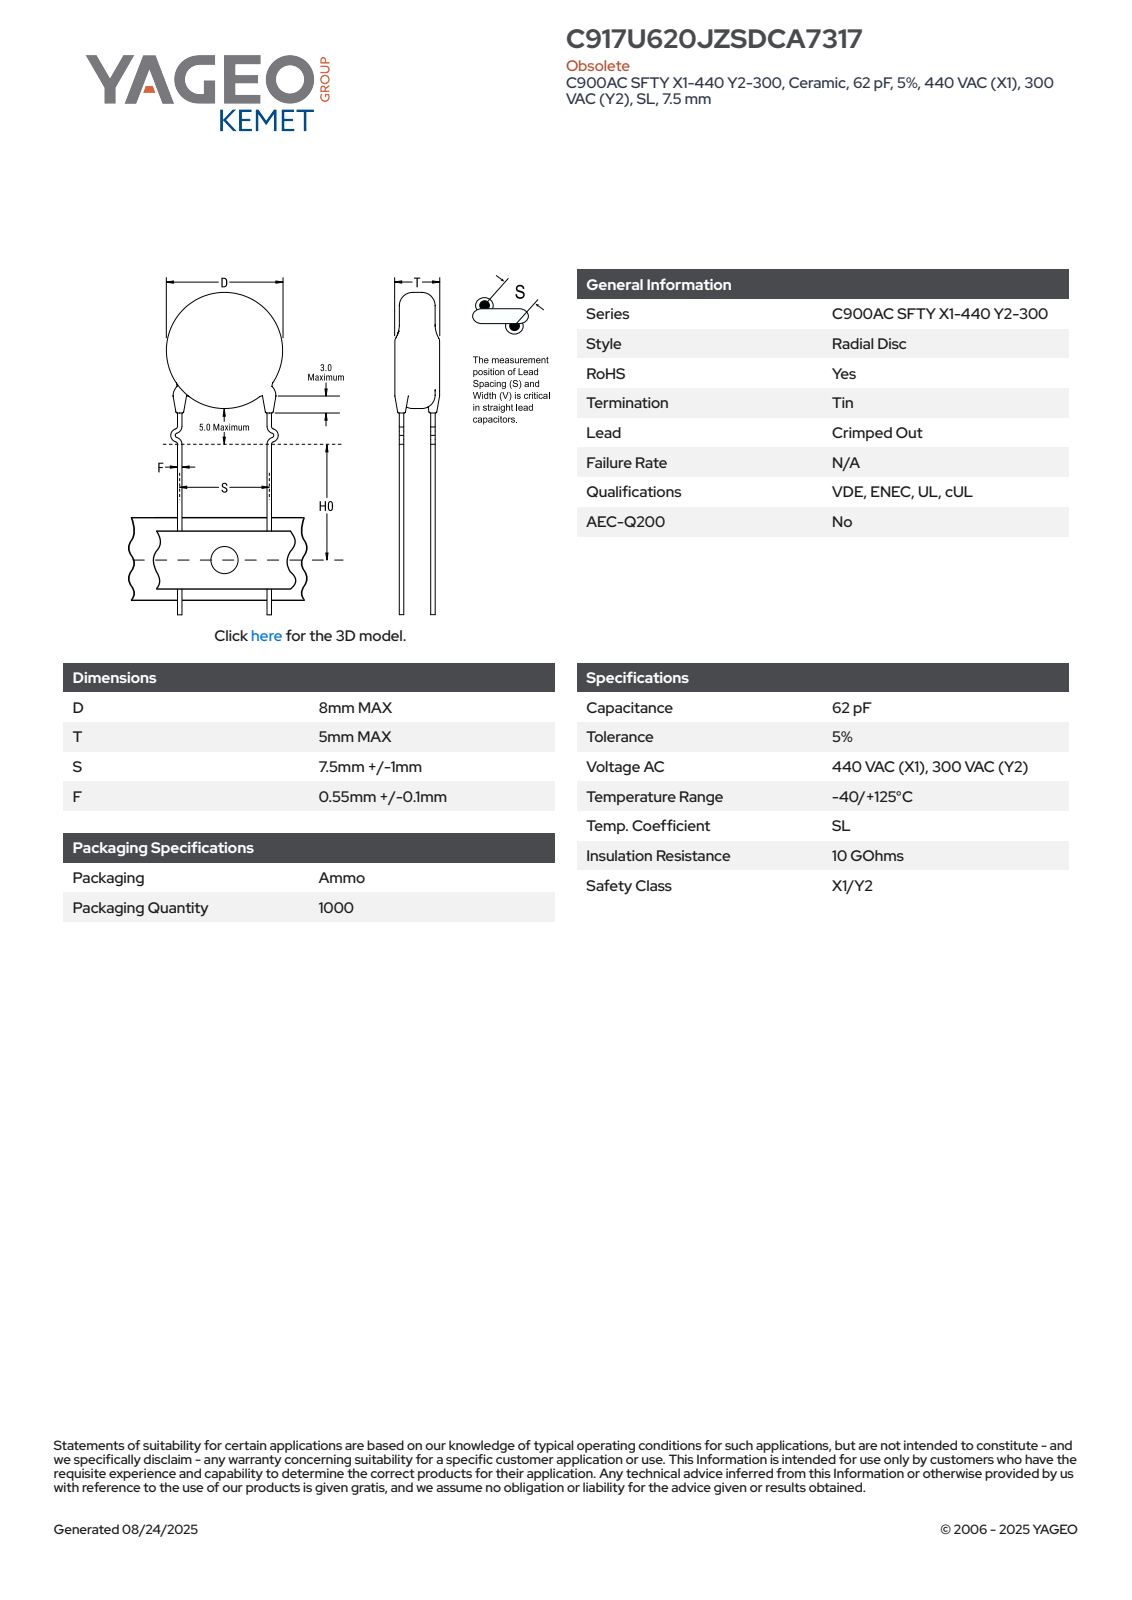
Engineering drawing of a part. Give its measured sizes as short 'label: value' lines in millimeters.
name: CCD_KCOC900_D8T5S7.5LL20F0.55
written by: SolidWorks 2014 (AUTOMOTIVE_DESIGN)
unit: mm
bodies: 4 solids, 87 faces (63 planar, 6 cylindrical, 18 other)
size: 33 × 12.09 × 5.04
volume: 264 mm³; area: 334 mm²
bosses: 2× ⌀1.2, 1× ⌀8
face distances: 5, 0.83, 4.42, 3.59, 3.39, 0.52, 0.31, 0.67, 1.71, 2.46
